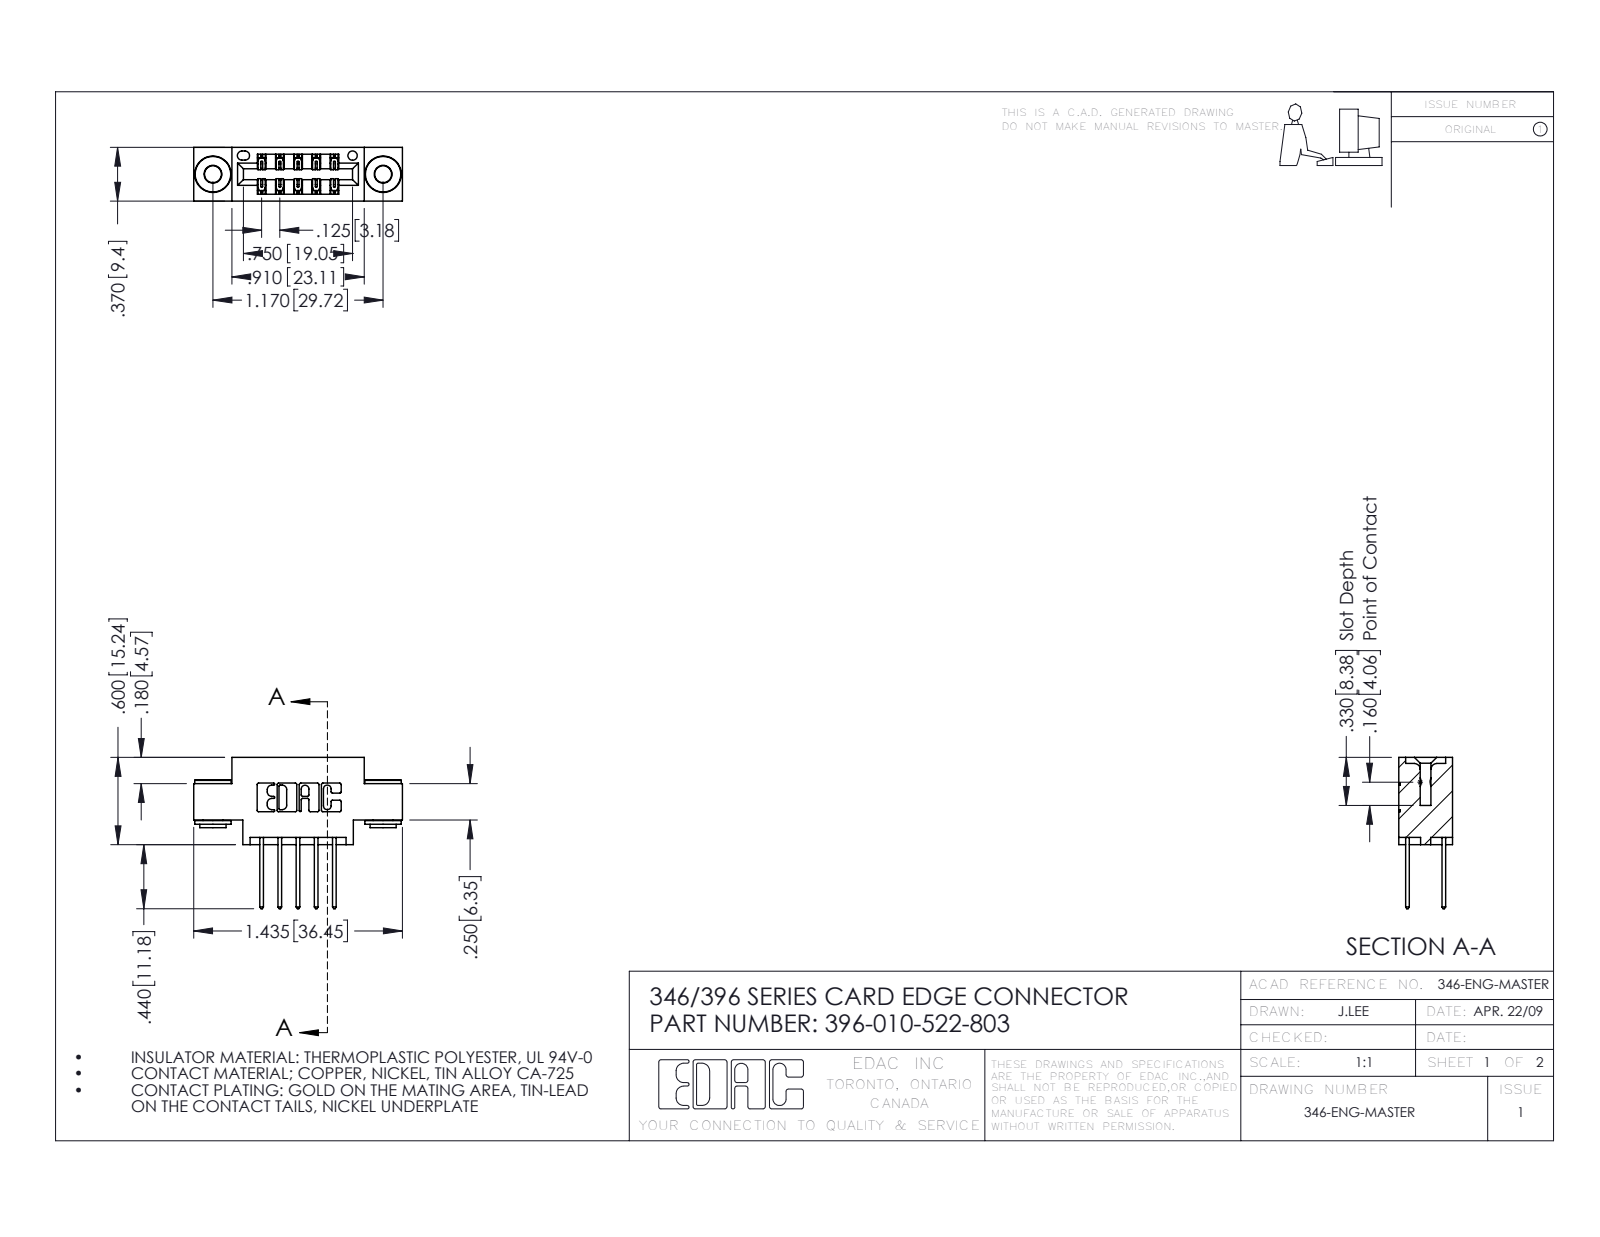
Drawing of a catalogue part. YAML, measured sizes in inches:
part_name: "345-292-001_345-293-122; 345-250-002_345-250-002-102; 396-010-522-803; 346 Part_0.170 Offset - 0.156 Dia-TH"
step_written_by: "SolidWorks 2016 (CONFIG_CONTROL_DESIGN)"
units: inches
bodies: {solids: 13, faces: 684, planar: 440, cylindrical: 236, other: 8}
overall_size: [1.435, 1.04, 0.37]
volume: 0.193
surface_area: 6.62
round_holes:
  - {diameter: 0.116, count: 2}
  - {diameter: 0.156, count: 2}
  - {diameter: 0.064, count: 1}
round_bosses_or_shafts:
  - {diameter: 0.25, count: 2}
  - {diameter: 0.18, count: 2}
  - {diameter: 0.136, count: 2}
partial_cylinders:
  - {radius: 0.01, count: 22}
  - {radius: 0.006, count: 15}
  - {radius: 0.01, count: 10}
  - {radius: 0.007, count: 6}
  - {radius: 0.031, count: 6}
  - {radius: 0.026, count: 3}
  - {radius: 0.014, count: 2}
  - {radius: 0.022, count: 2}
face_to_face_distances: [0.25, 0.37, 0.048, 0.322, 0.025, 0.275, 0.072, 0.298, 0.225, 0.148]
hole_center_spacings: [0.246, 0.969, 1.17]
